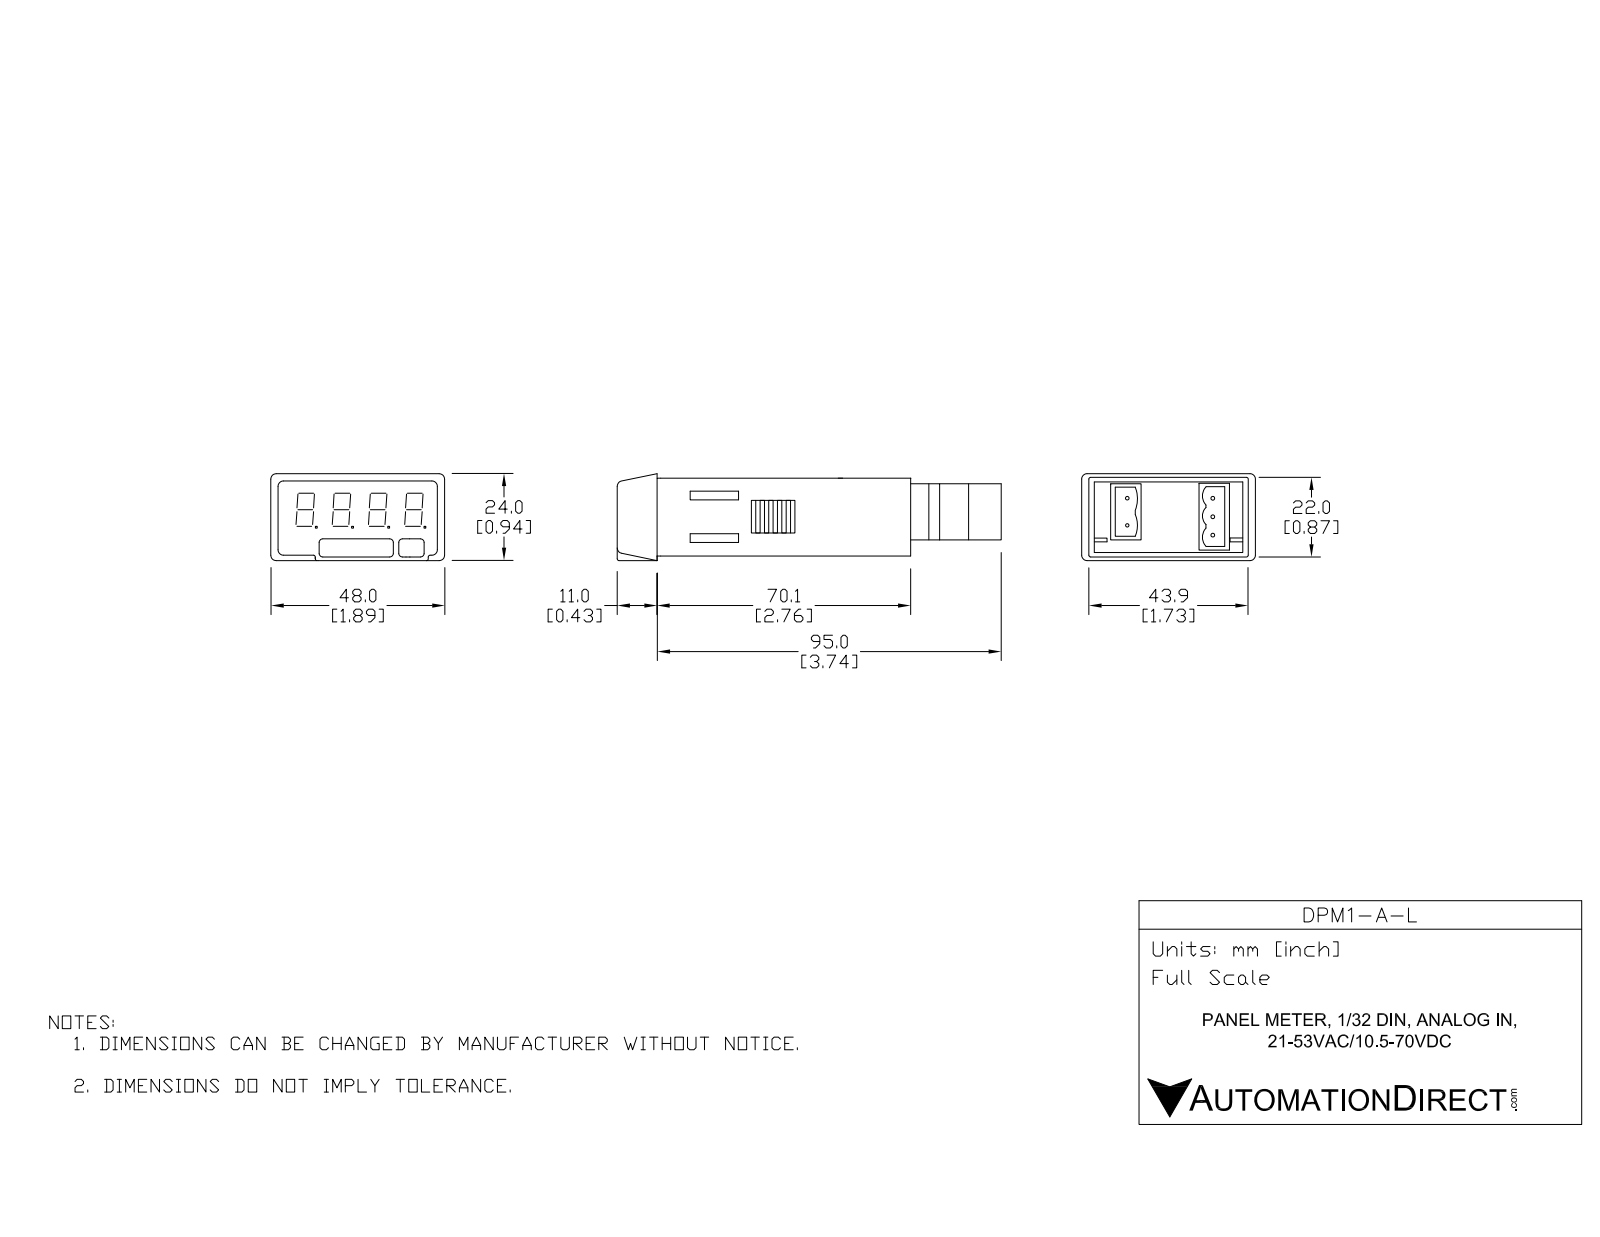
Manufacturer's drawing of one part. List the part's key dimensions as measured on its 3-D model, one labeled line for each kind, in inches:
Part name (STEP PRODUCT): DPM1-A-L
STEP written by: SolidWorks 2017 (AUTOMOTIVE_DESIGN)
Units: inches
Bodies: 3 solids, 852 faces (670 planar, 94 cylindrical, 88 other)
Overall size (bounding box): 4.169 × 1.89 × 0.945
Volume: 1.885 in³ · Surface area: 42.33 in²
Round holes (diameter × count): ⌀0.039 ×5, ⌀0.079 ×5, ⌀0.078 ×2, ⌀0.118 ×2, ⌀0.152 ×2
Partial cylindrical surfaces — rounded edges, fillets, slot ends (radius × count): R0.012 ×10, R0.014 ×10, R0.02 ×9, R0.07 ×5, R0.072 ×5, R0.039 ×4, R0.121 ×2, R0.025 ×1
Main face-to-face distances: 0.059, 0.807, 0.866, 0.748, 1.673, 1.732, 1.614, 3.185, 0.051, 3.134
Hole centre spacings: 0.138, 0.276, 0.413, 1.001, 1.006, 1.01, 1.028, 0.197
